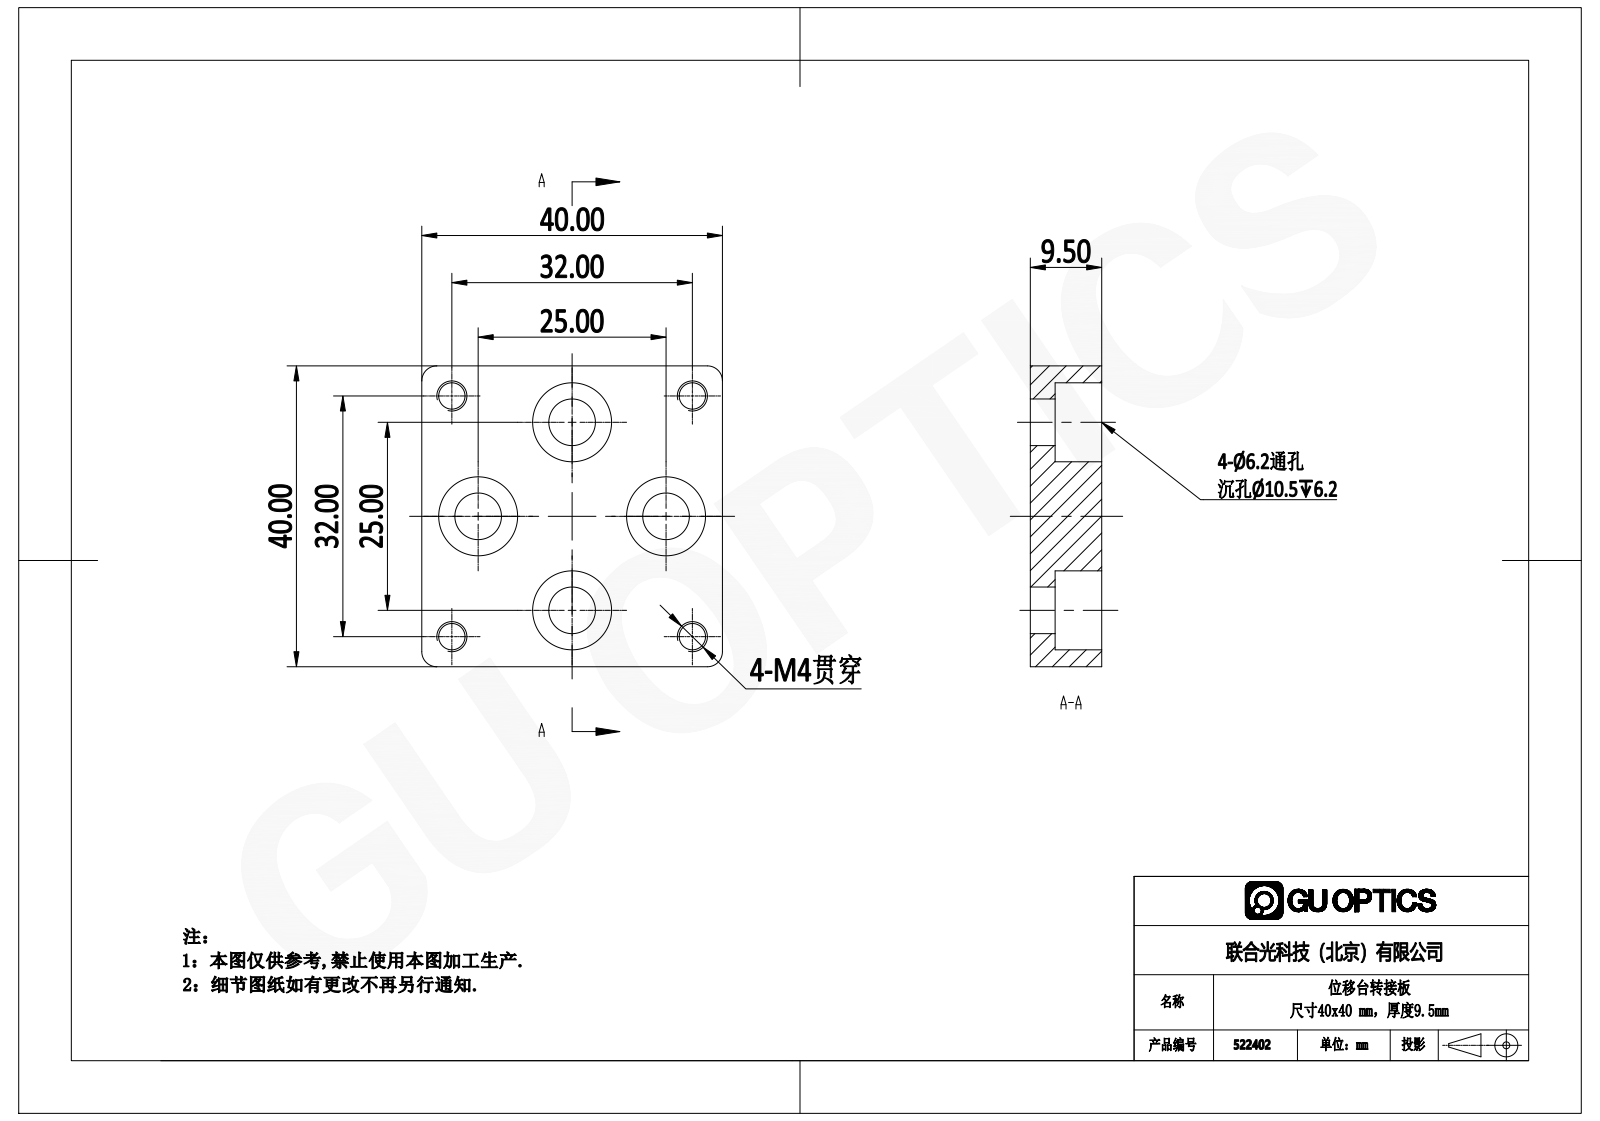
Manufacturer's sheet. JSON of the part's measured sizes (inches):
{"step_written_by": "SolidWorks 2020 (CONFIG_CONTROL_DESIGN)", "units": "inches", "bodies": {"solids": 1, "faces": 26, "planar": 10, "cylindrical": 16, "other": 0}, "overall_size": [1.575, 1.575, 0.374], "volume_in3": 0.748, "surface_area_in2": 9.075, "round_holes": [[0.138, 4], [0.244, 4], [0.413, 4]], "partial_cylinders_radius": [[0.079, 4]], "face_to_face_distances": [0.374, 1.575, 0.13, 0.244], "hole_center_spacings": [0.645, 1.287, 0.696, 1.26, 0.984, 1.781]}
